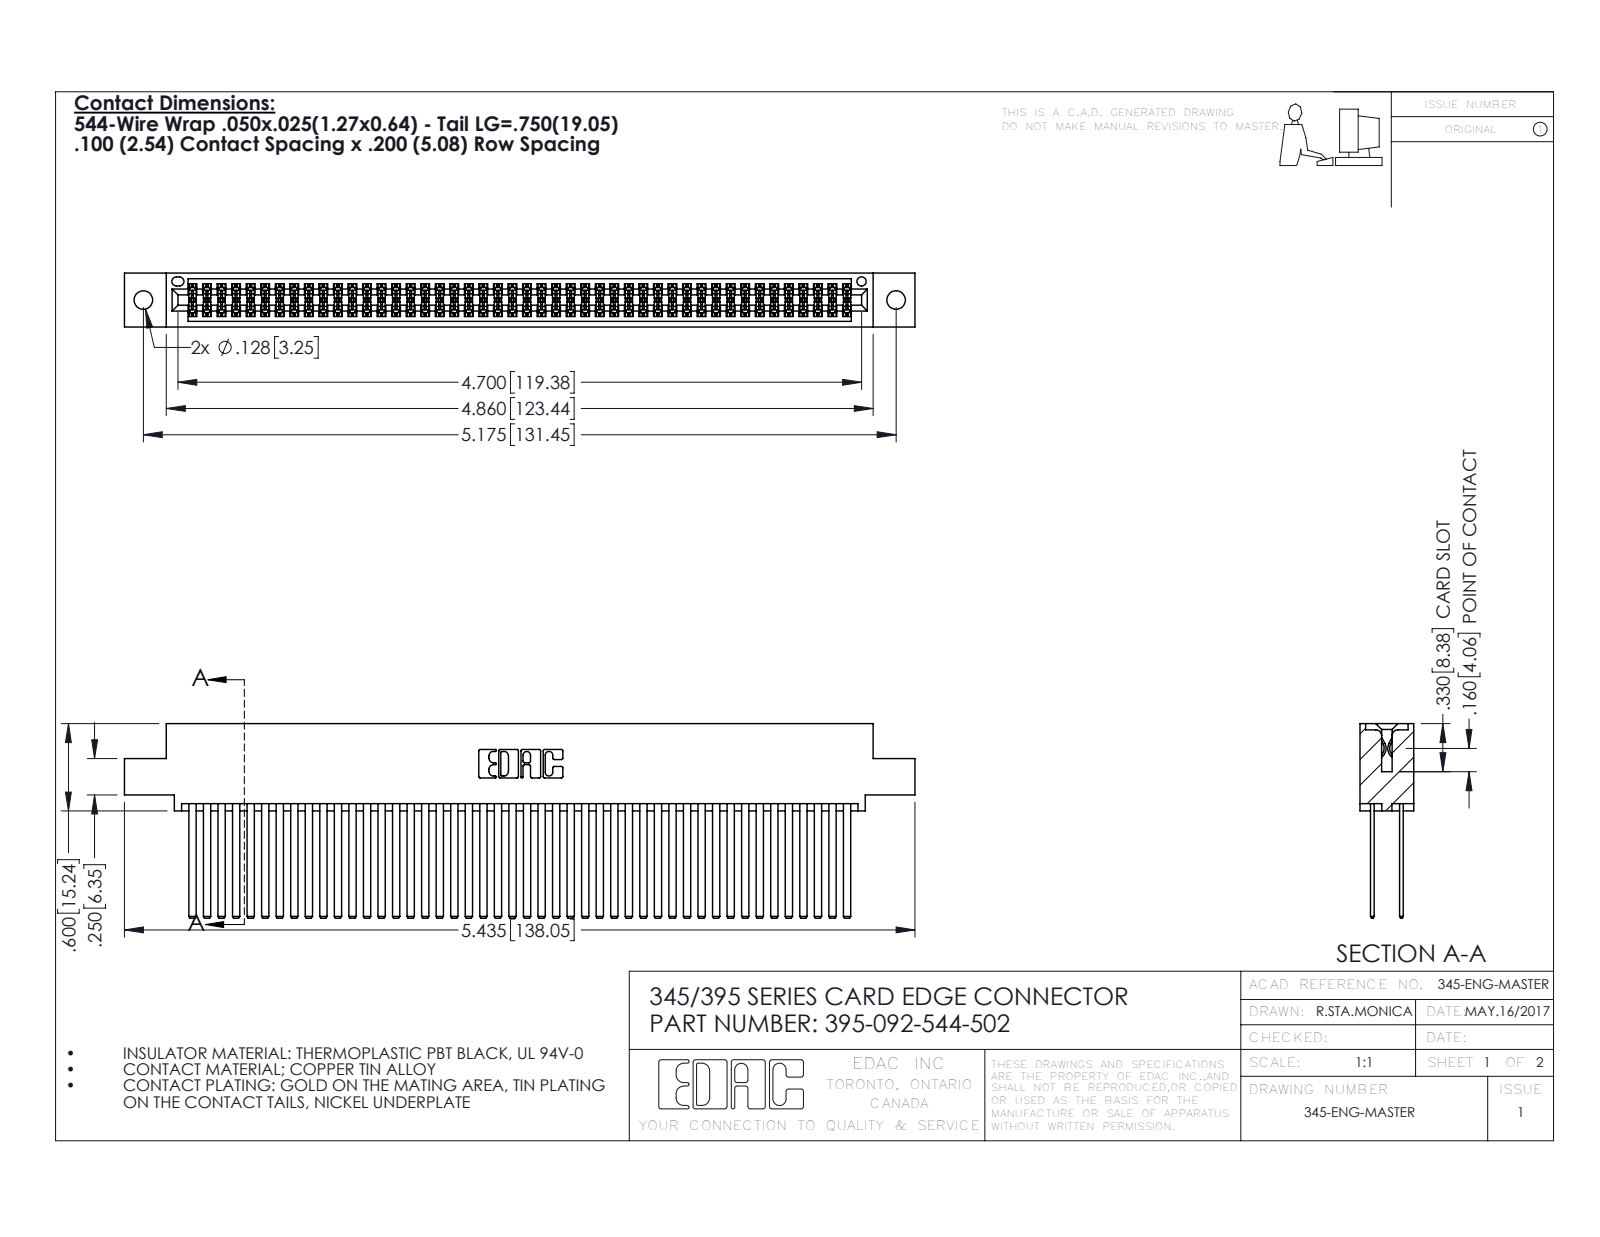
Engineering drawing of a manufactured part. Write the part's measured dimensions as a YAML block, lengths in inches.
part_name: "345 Part_0.110 Offset - 0.128 Dia; 395-092-544-502; 345-292-001_345-293-144"
step_written_by: "SolidWorks 2016 (CONFIG_CONTROL_DESIGN)"
units: inches
bodies: {solids: 93, faces: 4178, planar: 2752, cylindrical: 1426, other: 0}
overall_size: [5.435, 1.337, 0.37]
volume: 0.893
surface_area: 39.21
round_holes:
  - {diameter: 0.128, count: 2}
  - {diameter: 0.064, count: 1}
partial_cylinders:
  - {radius: 0.006, count: 138}
  - {radius: 0.01, count: 22}
  - {radius: 0.007, count: 6}
  - {radius: 0.031, count: 6}
  - {radius: 0.026, count: 3}
  - {radius: 0.014, count: 2}
  - {radius: 0.019, count: 2}
  - {radius: 0.022, count: 2}
face_to_face_distances: [0.2, 0.025, 0.072, 0.098, 0.272, 0.298, 0.225, 0.175, 0.37, 0.05]
hole_center_spacings: [0.27, 4.939, 5.175]
